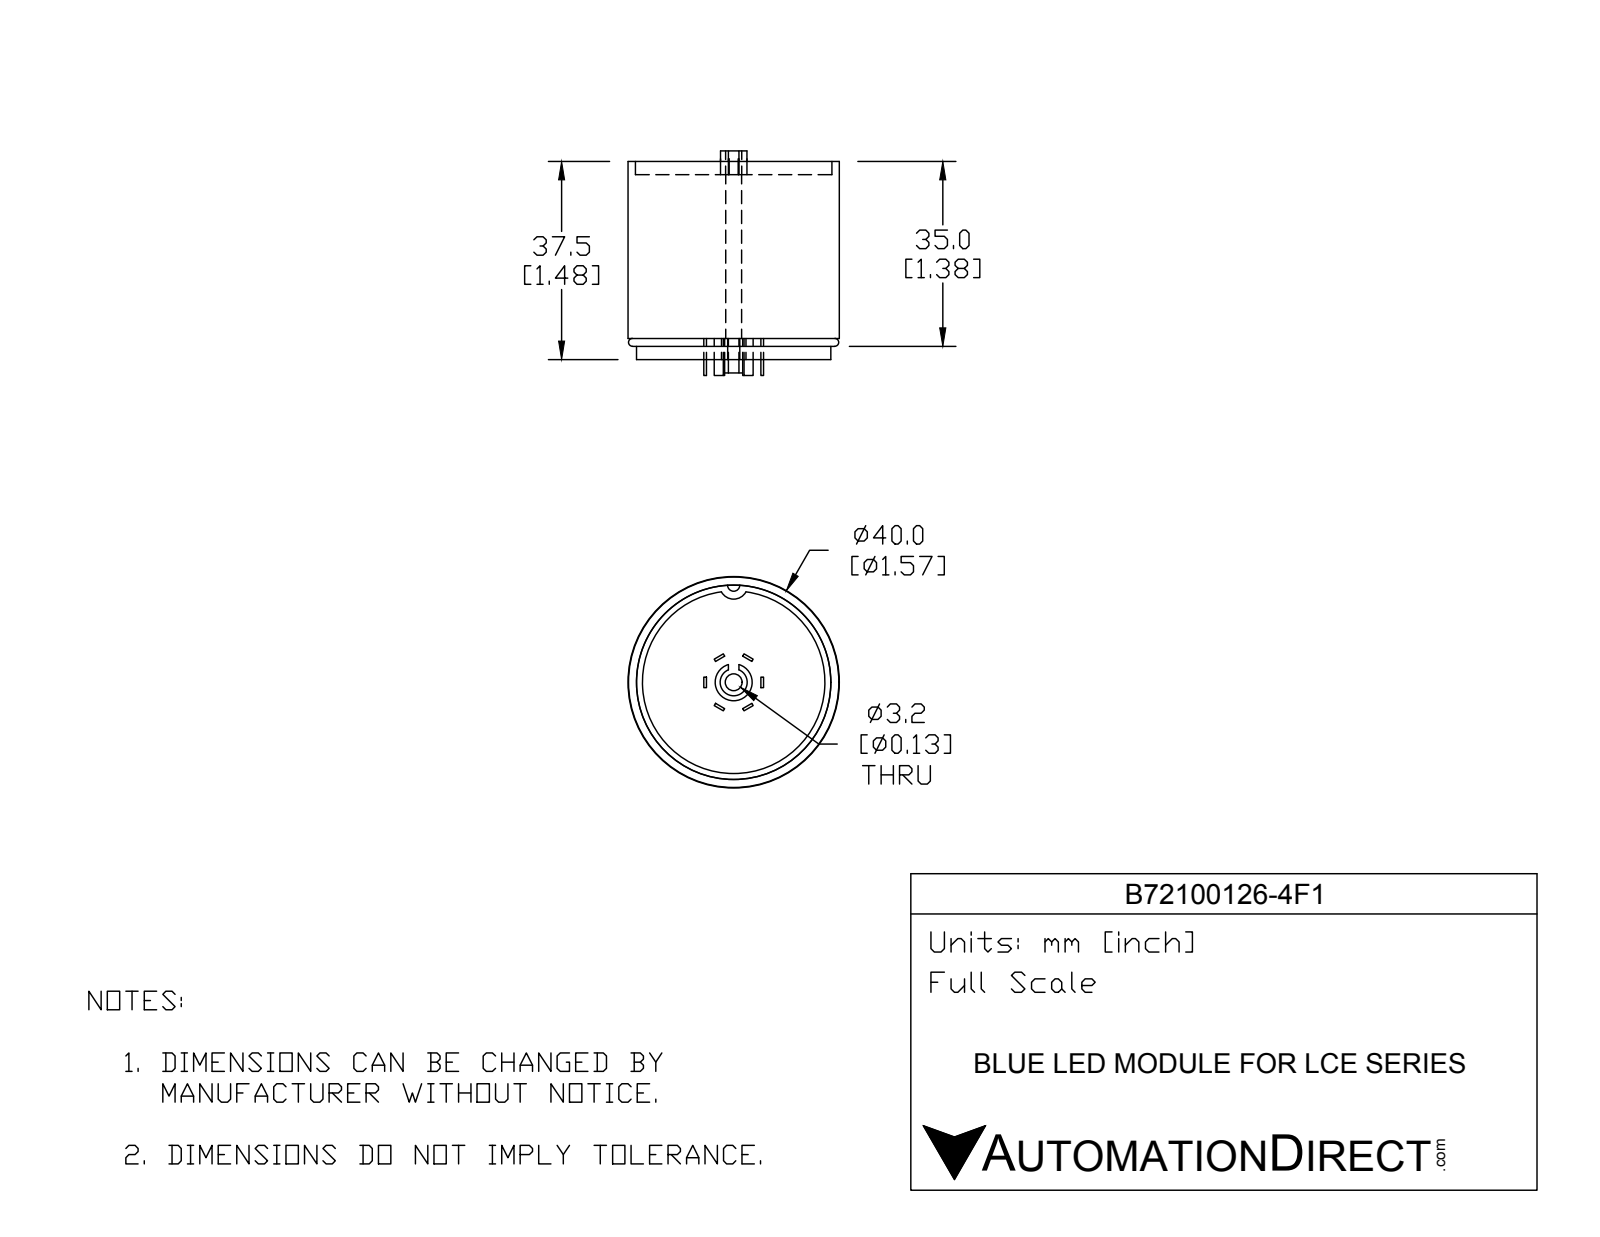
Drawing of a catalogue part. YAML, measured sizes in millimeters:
part_name: "B72100126-4F1"
step_written_by: "SolidWorks 2016 (AUTOMOTIVE_DESIGN)"
units: millimeters
bodies: {solids: 10, faces: 74, planar: 50, cylindrical: 20, other: 4}
overall_size: [43.02, 40, 40]
volume: 40201
surface_area: 9548
round_holes:
  - {diameter: 3, count: 1}
  - {diameter: 3.06, count: 1}
  - {diameter: 5.1, count: 1}
  - {diameter: 34.54, count: 1}
  - {diameter: 37.2, count: 1}
round_bosses_or_shafts:
  - {diameter: 40, count: 1}
  - {diameter: 36.8, count: 1}
  - {diameter: 7, count: 1}
  - {diameter: 5, count: 1}
partial_cylinders:
  - {radius: 0.9, count: 1}
  - {radius: 1.15, count: 1}
  - {radius: 2.65, count: 1}
face_to_face_distances: [31, 34, 3, 4, 35, 38, 0.5, 10.8, 2, 11.3]
